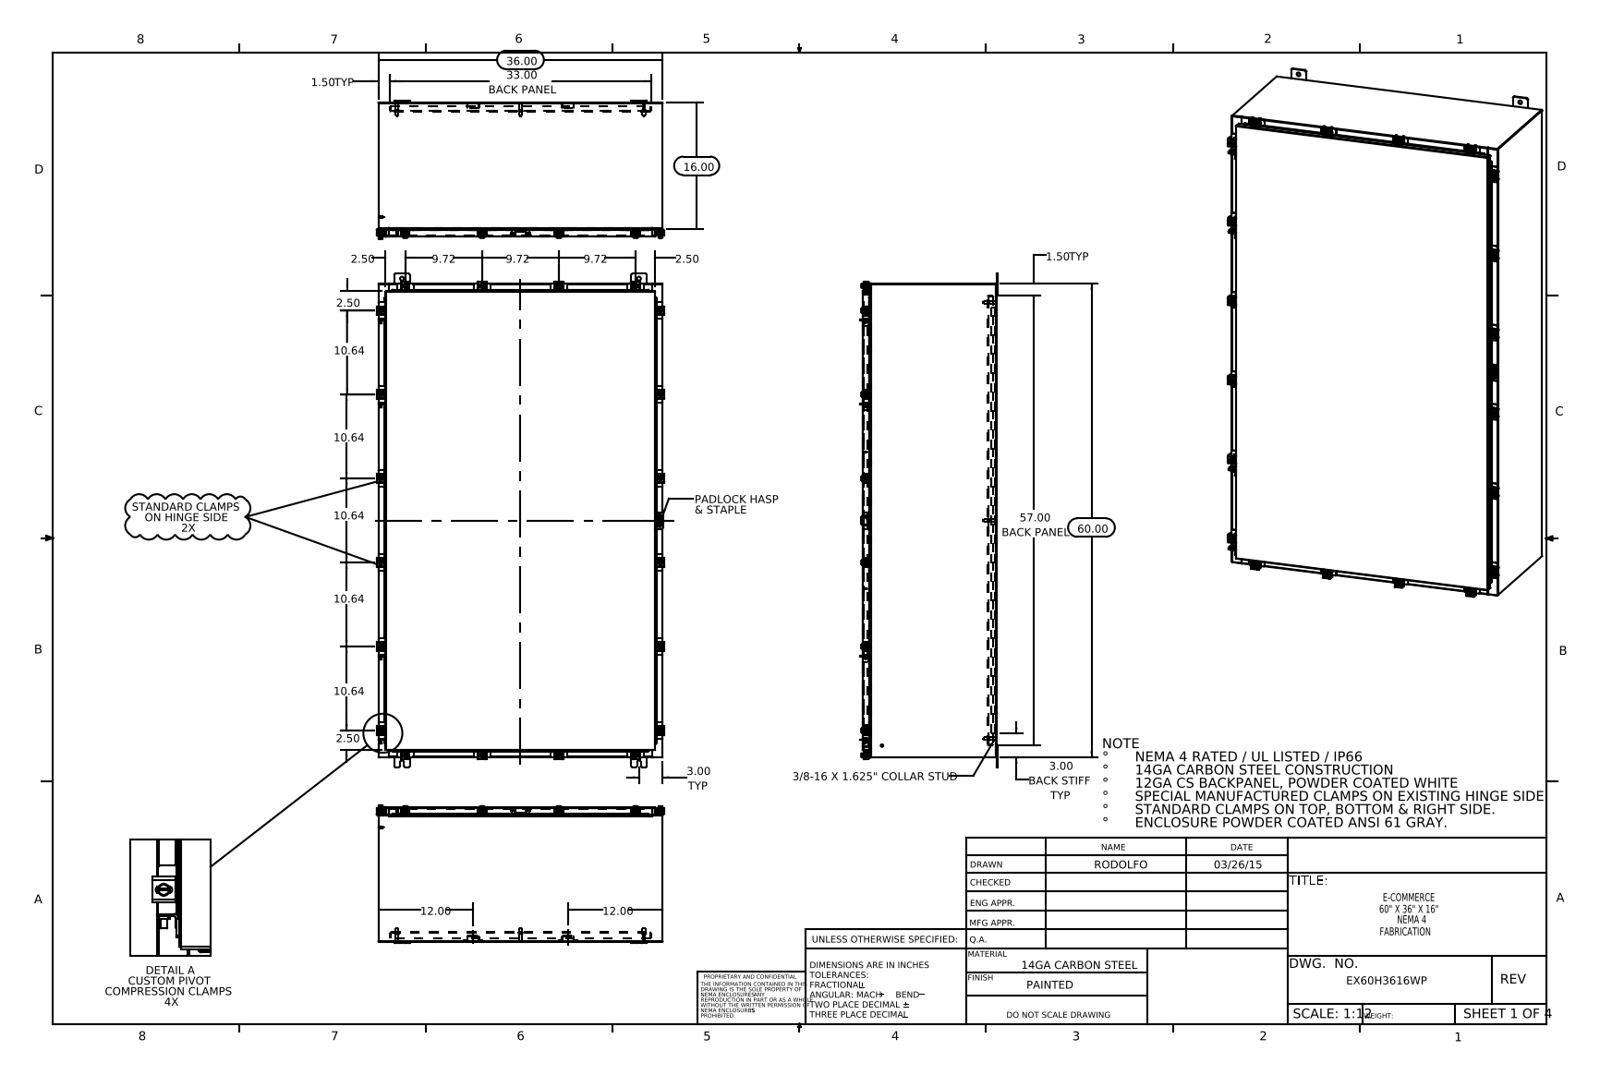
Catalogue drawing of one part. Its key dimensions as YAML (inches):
part_name: "EX60H3616WP Clamp Bracket; 30X10 Clamp Bracket2; EX60H3616WP Clamp Assembly; EX60H3616WP Special Clamp (+8 more)"
step_written_by: "SolidWorks 2014 (CONFIG_CONTROL_DESIGN)"
units: inches
bodies: {solids: 140, faces: 3424, planar: 1773, cylindrical: 1319, other: 332}
overall_size: [62.5, 36.421, 17.453]
volume: 850
surface_area: 21217
round_holes:
  - {diameter: 0.213, count: 20}
  - {diameter: 0.26, count: 20}
  - {diameter: 0.5, count: 12}
  - {diameter: 0.25, count: 9}
  - {diameter: 0.125, count: 1}
round_bosses_or_shafts:
  - {diameter: 0.5, count: 20}
  - {diameter: 0.25, count: 20}
  - {diameter: 0.399, count: 16}
  - {diameter: 0.625, count: 8}
  - {diameter: 0.375, count: 8}
  - {diameter: 0.33, count: 8}
  - {diameter: 0.157, count: 8}
  - {diameter: 0.14, count: 8}
partial_cylinders:
  - {radius: 0.06, count: 84}
  - {radius: 0.141, count: 40}
  - {radius: 0.013, count: 38}
  - {radius: 0.12, count: 36}
  - {radius: 0.088, count: 34}
  - {radius: 0.09, count: 32}
  - {radius: 0.05, count: 29}
  - {radius: 0.145, count: 28}
face_to_face_distances: [0.075, 16.9, 16.826, 0.104, 16.975, 35.925, 1, 1.075, 15.826, 15.9]
hole_center_spacings: [1.969, 2.224, 2.347, 13.972, 14.729, 16.126, 27.625, 29.744]
